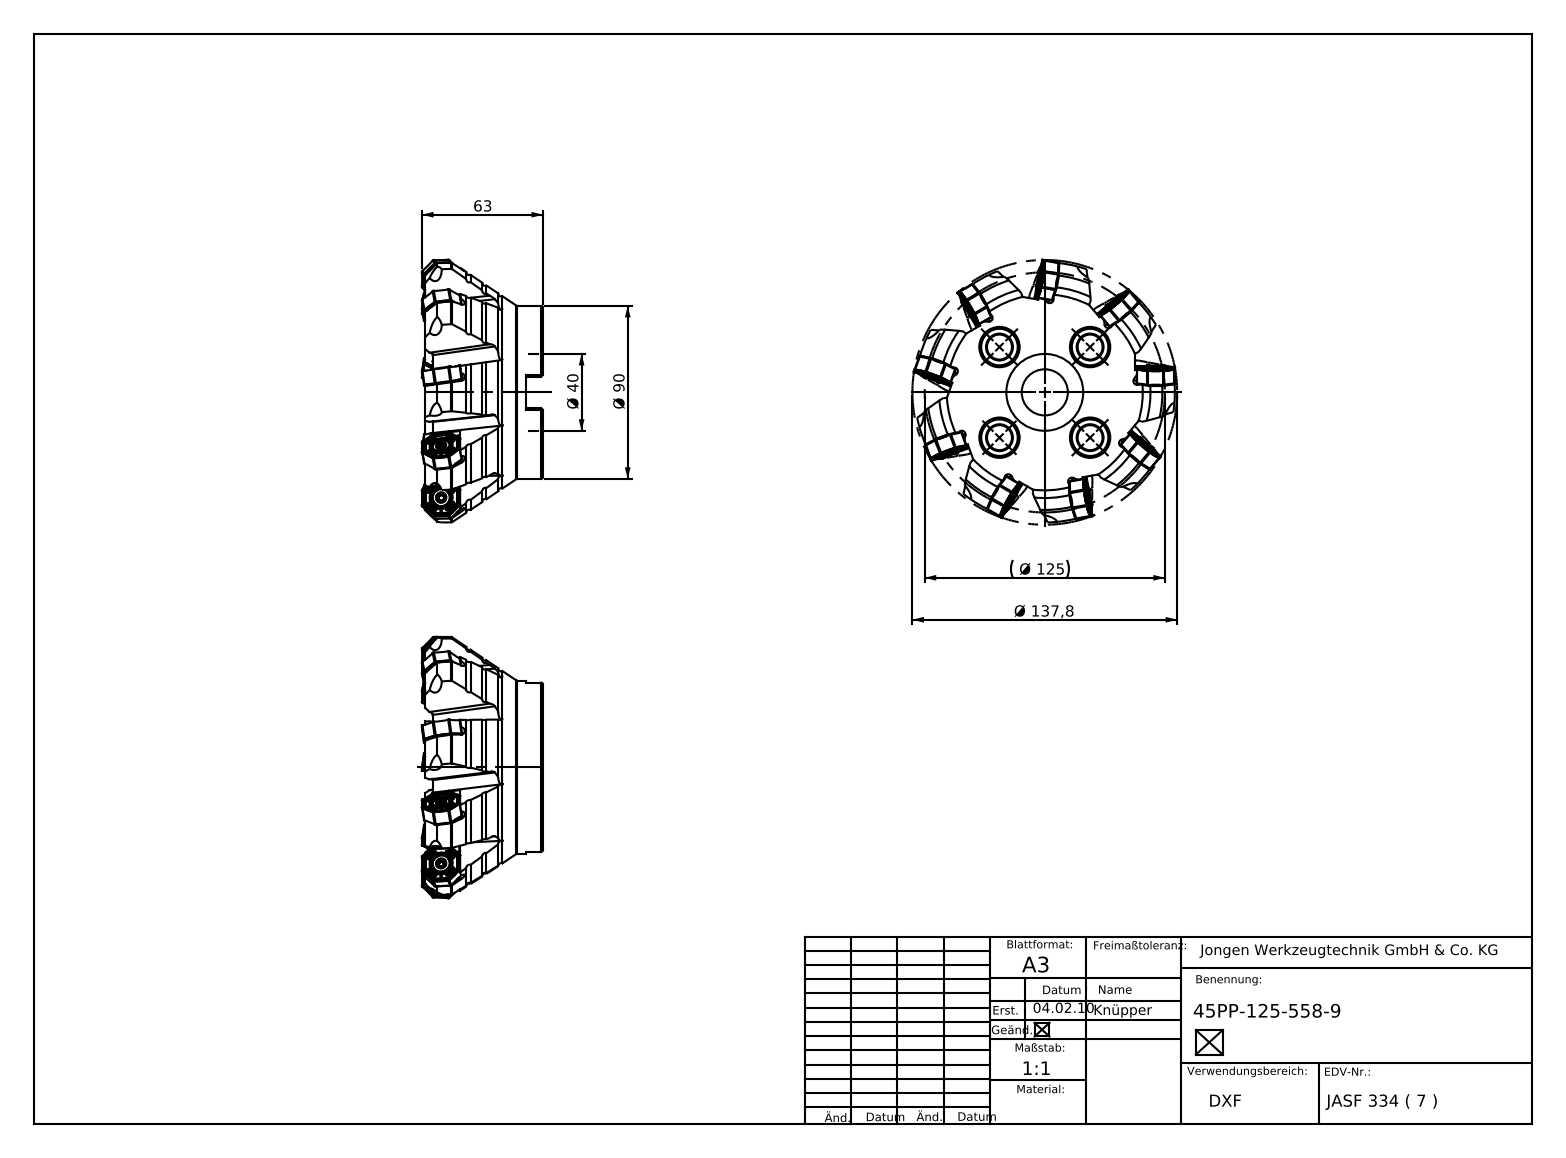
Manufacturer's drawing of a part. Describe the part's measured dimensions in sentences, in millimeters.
The part is named "45PP-125-558-9". Its 3-D file was written by "SolidWorks 2013 (AUTOMOTIVE_DESIGN)". It is 1 solid with 558 faces: 188 planar, 116 cylindrical and 254 other. Overall it measures 137.8 by 137.8 by 62.99 millimeters. Its volume is 471 953 cubic millimeters and its surface area 68 900 square millimeters. Round holes: 4 of diameter 13, 4 of diameter 20, 1 of diameter 24, 1 of diameter 40, 1 of diameter 40.15, 1 of diameter 40.3. Round bosses or shafts: 1 of diameter 90. Partial cylindrical surfaces (rounded edges, fillets, slot ends): 18 of radius 0.5, 18 of radius 1.5, 18 of radius 2, 1 of radius 67.7. The main face-to-face distances are 57.5, 9, 48.5, 28, 19, 29.5, 28.5, 19.5, 0.5, 29. The hole center spacings are 33.35, 47.16, 66.69.
